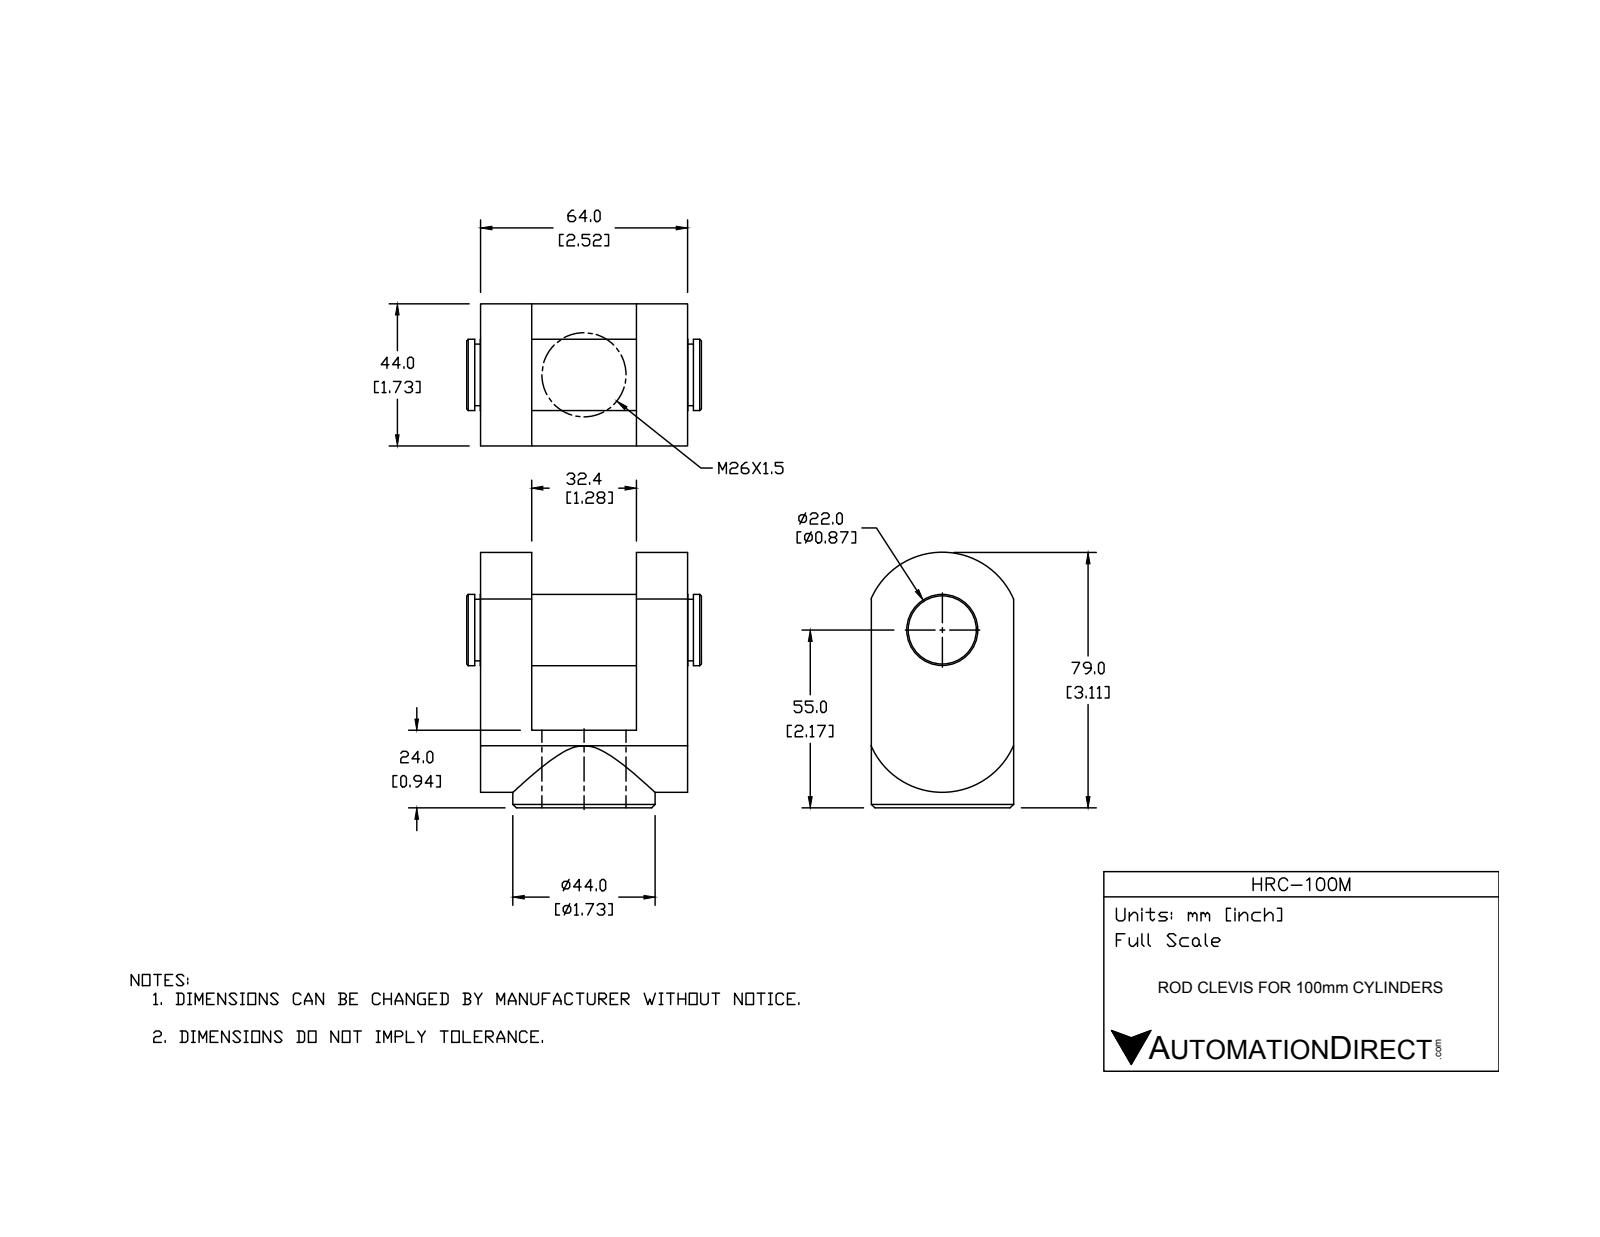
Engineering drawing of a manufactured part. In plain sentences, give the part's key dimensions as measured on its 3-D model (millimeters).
The part is named "HRC-100M". Its 3-D file was written by "SolidWorks 2015 (CONFIG_CONTROL_DESIGN)". It is 2 solids with 46 faces: 14 planar, 22 cylindrical and 10 other. Overall it measures 79 by 72.6 by 44 millimeters. Its volume is 129 128 cubic millimeters and its surface area 29 023 square millimeters. Round holes: 1 of diameter 24.5. Round bosses or shafts: 1 of diameter 44, 1 of diameter 22, 1 of diameter 19. Partial cylindrical surfaces (rounded edges, fillets, slot ends): 2 of radius 24. The main face-to-face distances are 15.8, 48.2, 64, 32.4, 44, 24, 4.3, 20.1, 52.5, 68.3.
